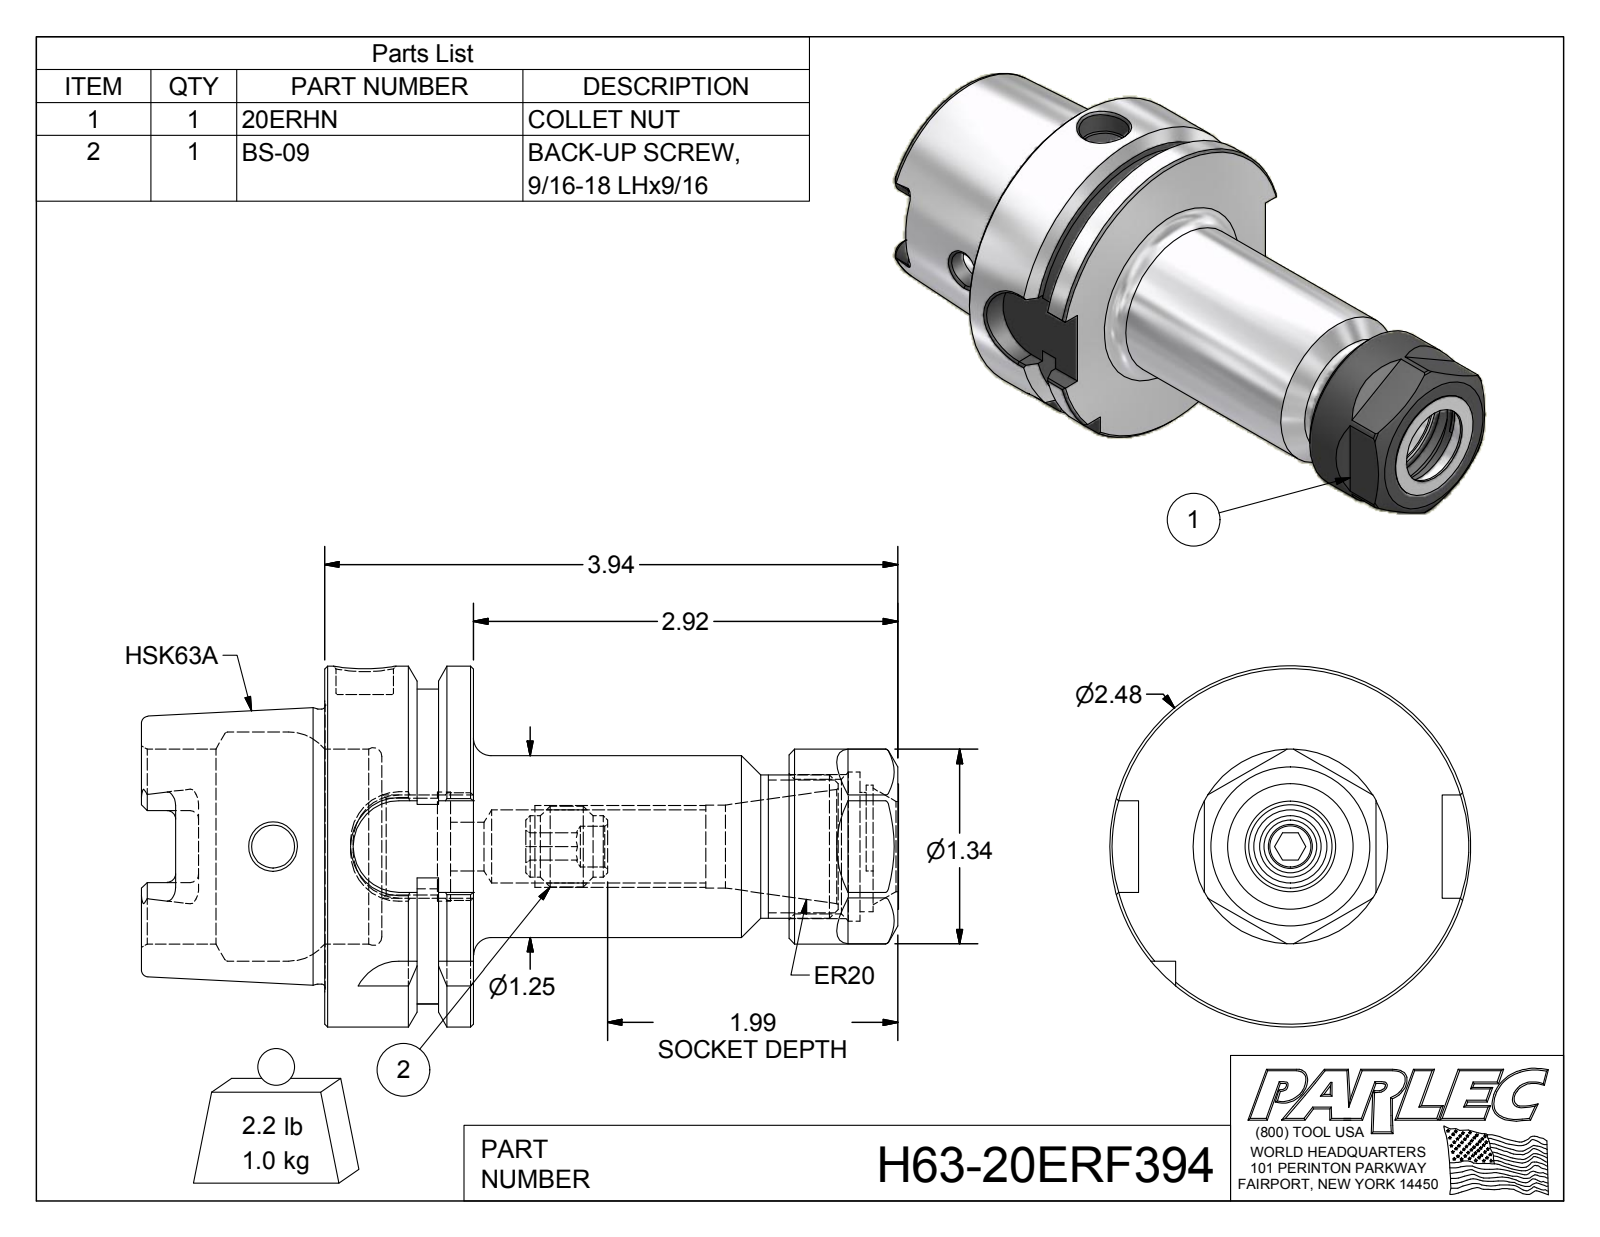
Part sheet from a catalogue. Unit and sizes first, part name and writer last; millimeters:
Units: millimetres
Overall size (bounding box): 132.08 × 63 × 63
Round holes (diameter × count): ⌀7.14 ×1, ⌀7.5 ×1, ⌀8.5 ×1, ⌀10 ×1, ⌀12.75 ×1, ⌀14.48 ×1, ⌀15.49 ×1, ⌀16.92 ×1, ⌀19.02 ×1, ⌀23.5 ×1, ⌀26 ×1, ⌀34 ×1
Round bosses / shafts (diameter × count): ⌀63 ×1, ⌀48.04 ×1, ⌀31.75 ×1, ⌀25 ×1, ⌀14.1 ×1, ⌀10.72 ×1
Partial cylindrical surfaces — rounded edges, fillets, slot ends (radius × count): R1.5 ×6, R2.88 ×4, R8 ×4, R9.47 ×1, R10.55 ×1, R10.75 ×1, R27.5 ×1
Main face-to-face distances: 26, 6.12, 9.88, 10, 16, 100.08, 90.08, 74.08, 32, 30
Volume: 126 495 mm³ · Surface area: 36 370 mm²
Bodies: 3 solids, 198 faces (83 planar, 48 cylindrical, 67 other)
Part name (STEP PRODUCT): H63-20ER4-1; 20ERHN; BS-09; H63-20ERF394
STEP written by: Autodesk Inventor 2016 (AUTOMOTIVE_DESIGN)
